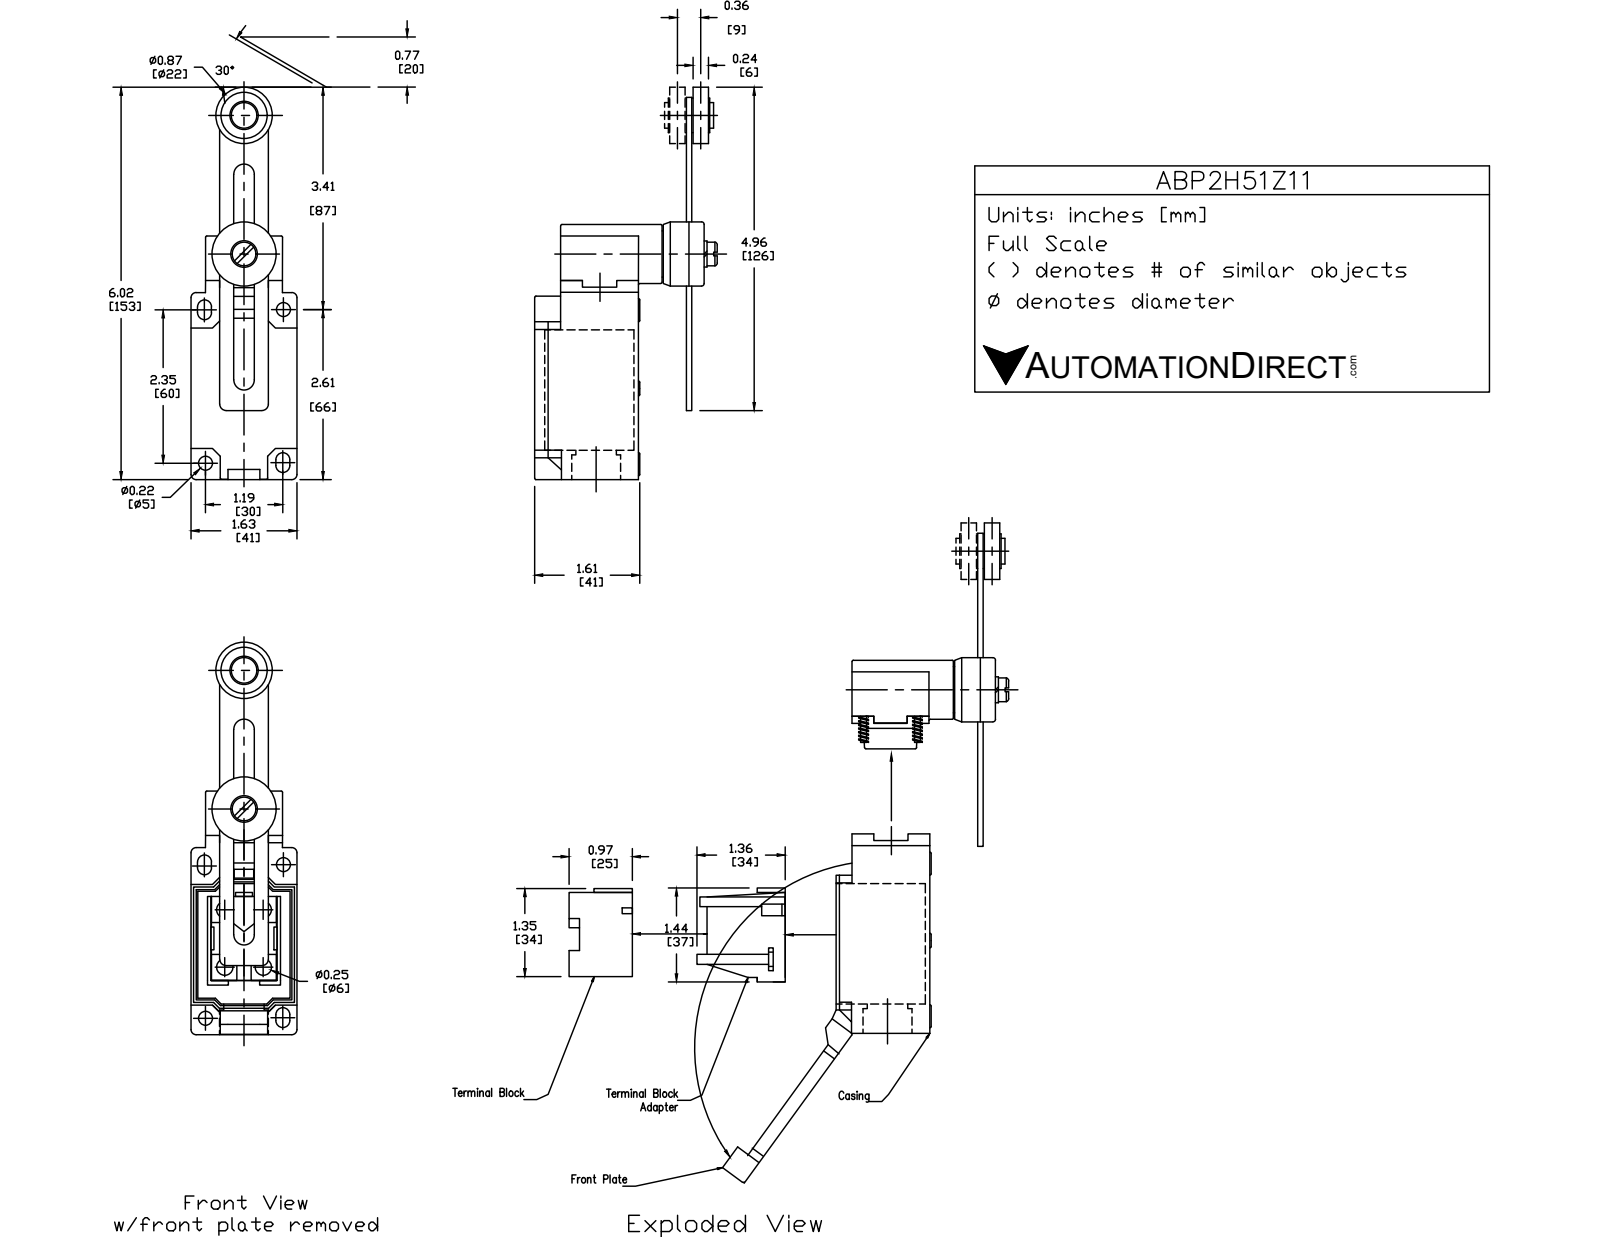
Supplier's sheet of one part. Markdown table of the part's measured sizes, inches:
| quantity | value |
| --- | --- |
| part name | ABP2H51Z11 |
| STEP written by | SolidWorks 2017 (AUTOMOTIVE_DESIGN) |
| units | inches |
| bodies | 7 solids, 248 faces (135 planar, 91 cylindrical, 22 other) |
| overall size | 6.39 × 2.414 × 1.614 |
| volume | 8.883 in³ |
| surface area | 50.28 in² |
| round holes (diameter × count) | 0.213 × 2, 0.236 × 1, 0.551 × 1, 0.669 × 1, 0.748 × 1 |
| round bosses / shafts (diameter × count) | 0.354 × 5, 0.394 × 2, 0.984 × 1, 0.906 × 1, 0.866 × 1, 0.709 × 1, 0.276 × 1 |
| partial cylindrical surfaces (radius × count) | 0.02 × 16, 0.079 × 4, 0.106 × 4, 0.118 × 2, 0.159 × 2, 0.276 × 1, 0.453 × 1, 0.472 × 1 |
| main face-to-face distances | 1.614, 1.565, 0.435, 0.079, 1.921, 0.356, 2, 1.181, 0.217, 1.398 |
| hole center spacings | 1.042, 2.641, 3.274 |
